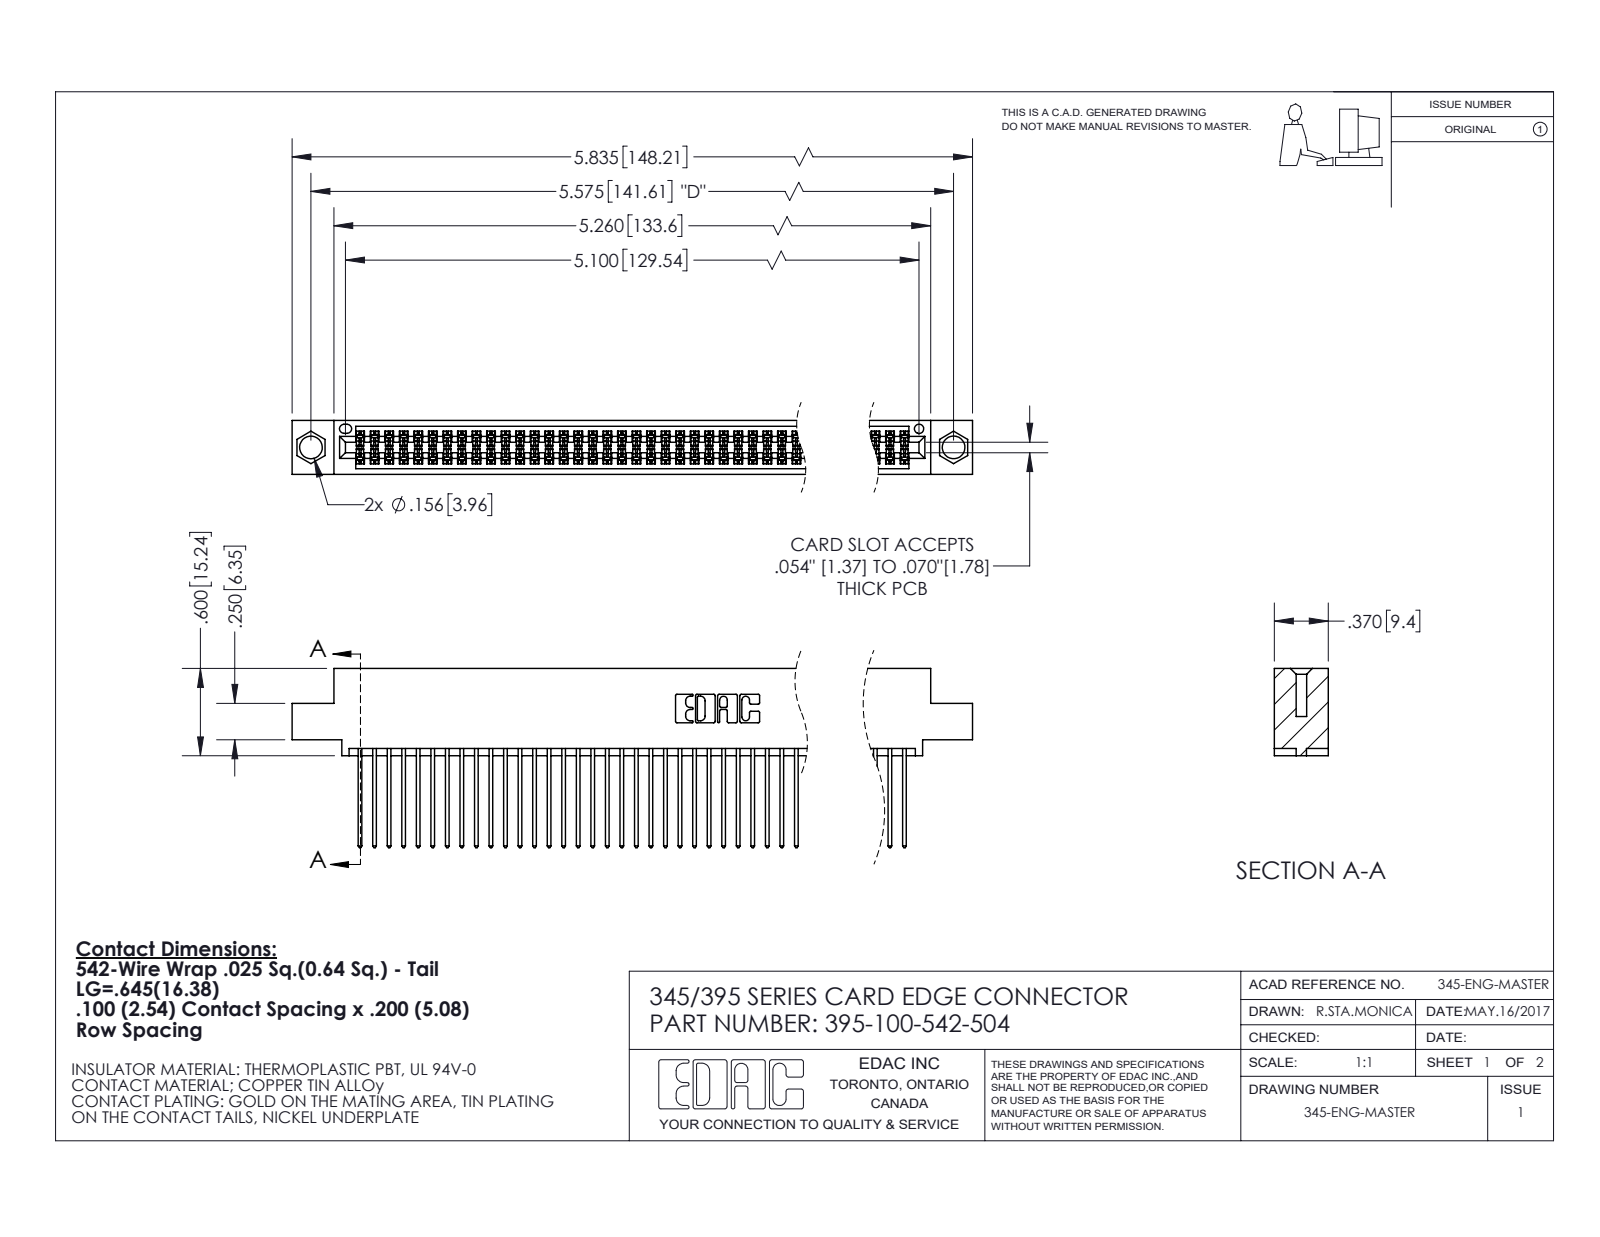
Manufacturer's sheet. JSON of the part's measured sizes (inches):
{"part_name": "345-292-001_345-293-142; 395-100-542-504; 345 Part_0.110 Offset - 0.156 Dia-TI", "step_written_by": "SolidWorks 2020 (CONFIG_CONTROL_DESIGN)", "units": "inches", "bodies": {"solids": 101, "faces": 5144, "planar": 3398, "cylindrical": 1746, "other": 0}, "overall_size": [5.835, 1.232, 0.37], "volume_in3": 0.901, "surface_area_in2": 37.34, "round_holes": [[0.156, 2], [0.064, 1]], "partial_cylinders_radius": [[0.006, 150], [0.01, 100], [0.01, 22], [0.007, 6], [0.031, 6], [0.026, 3], [0.014, 2], [0.019, 2]], "face_to_face_distances": [0.072, 0.298, 0.2, 0.098, 0.272, 0.025, 0.225, 0.37, 0.175, 0.149], "hole_center_spacings": [0.27, 5.339, 5.575]}
